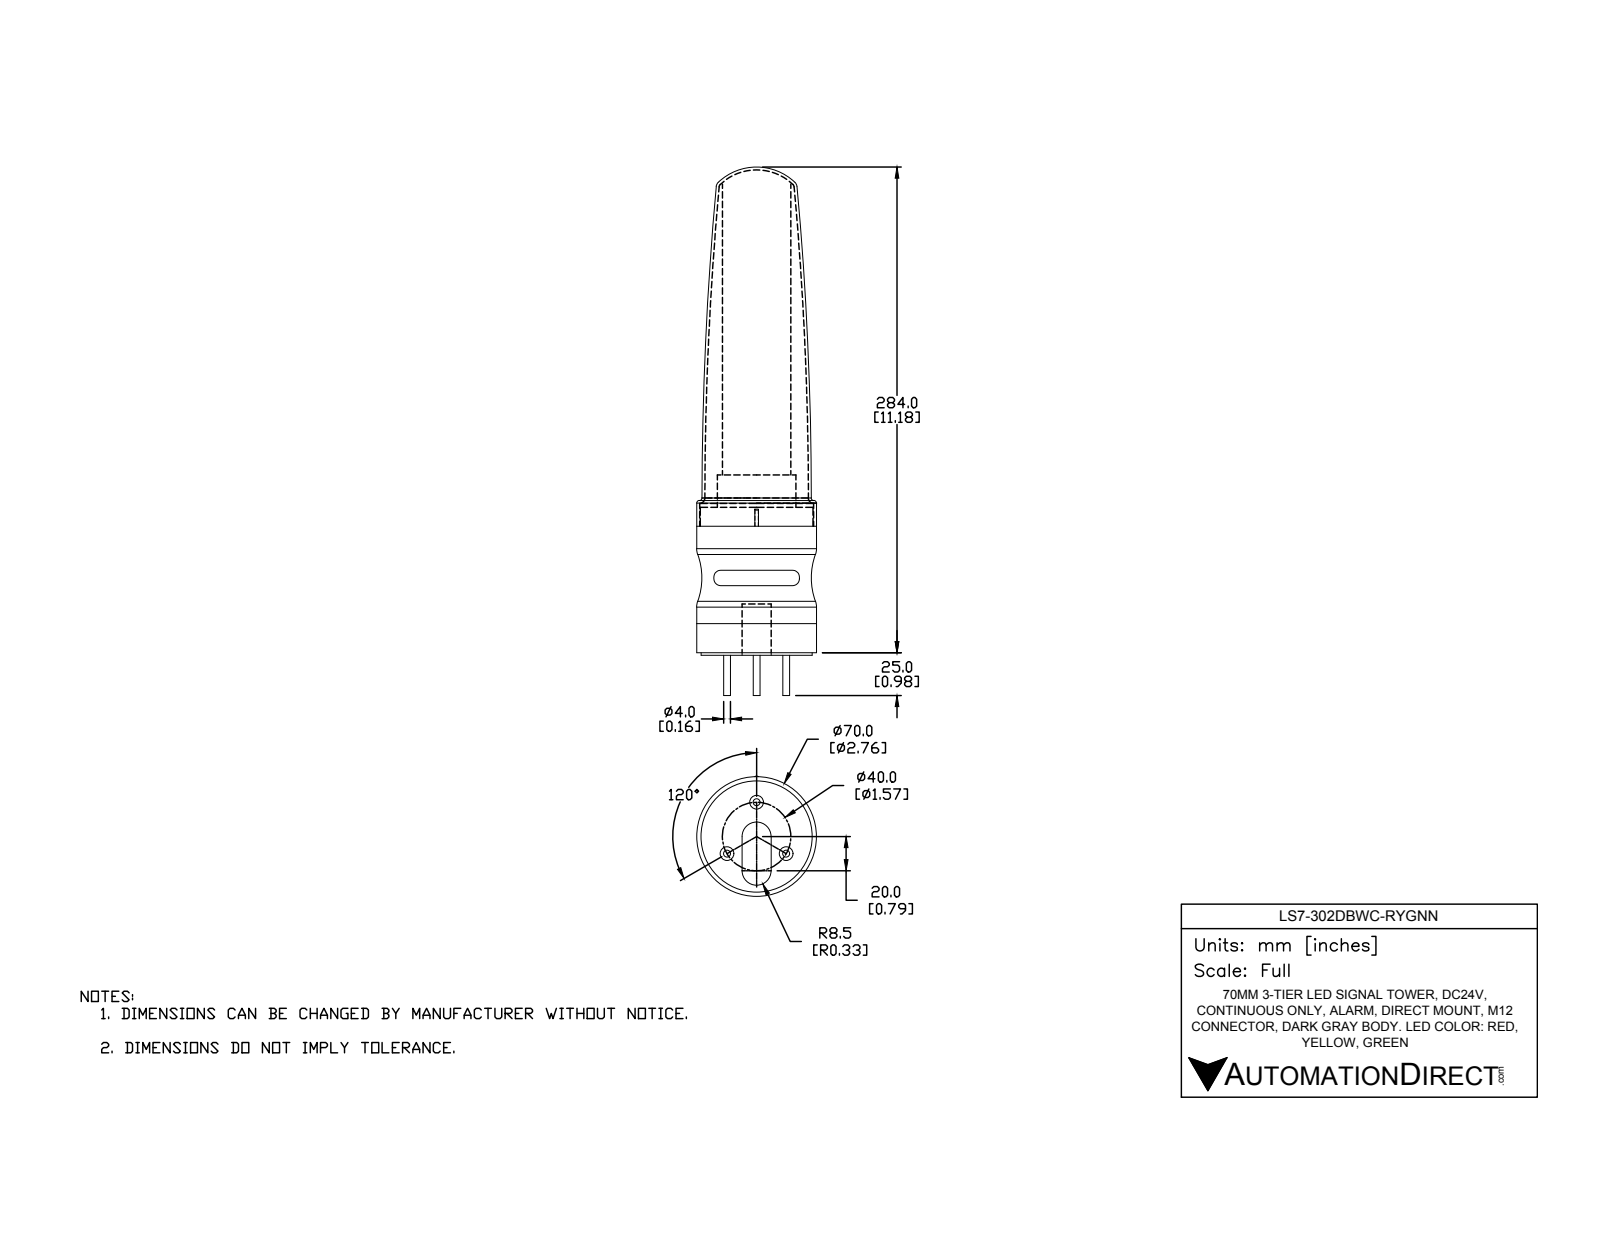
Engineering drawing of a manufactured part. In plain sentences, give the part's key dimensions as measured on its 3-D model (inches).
The part is named "LS7-302DBWC-RYGNN". Its 3-D file was written by "SolidWorks 2016 (AUTOMOTIVE_DESIGN)". It is 8 solids with 101 faces: 32 planar, 45 cylindrical and 24 other. Overall it measures 12.165 by 2.768 by 2.756 inches. Its volume is 36.36 cubic inches and its surface area 230.6 square inches. Round holes: 3 of diameter 0.315, 1 of diameter 2.622. Round bosses or shafts: 3 of diameter 0.157, 1 of diameter 2.756, 1 of diameter 2.598, 1 of diameter 2.559, 1 of diameter 1.811, 1 of diameter 1.575. Partial cylindrical surfaces (rounded edges, fillets, slot ends): 4 of radius 0.157, 2 of radius 0.335, 1 of radius 0.039, 1 of radius 0.079. The main face-to-face distances are 0.669, 4.094, 3.425, 0.059, 0.728, 4.154, 3.406, 3.346, 2.677, 0.748. The hole center spacings are 0.787, 1.364.
